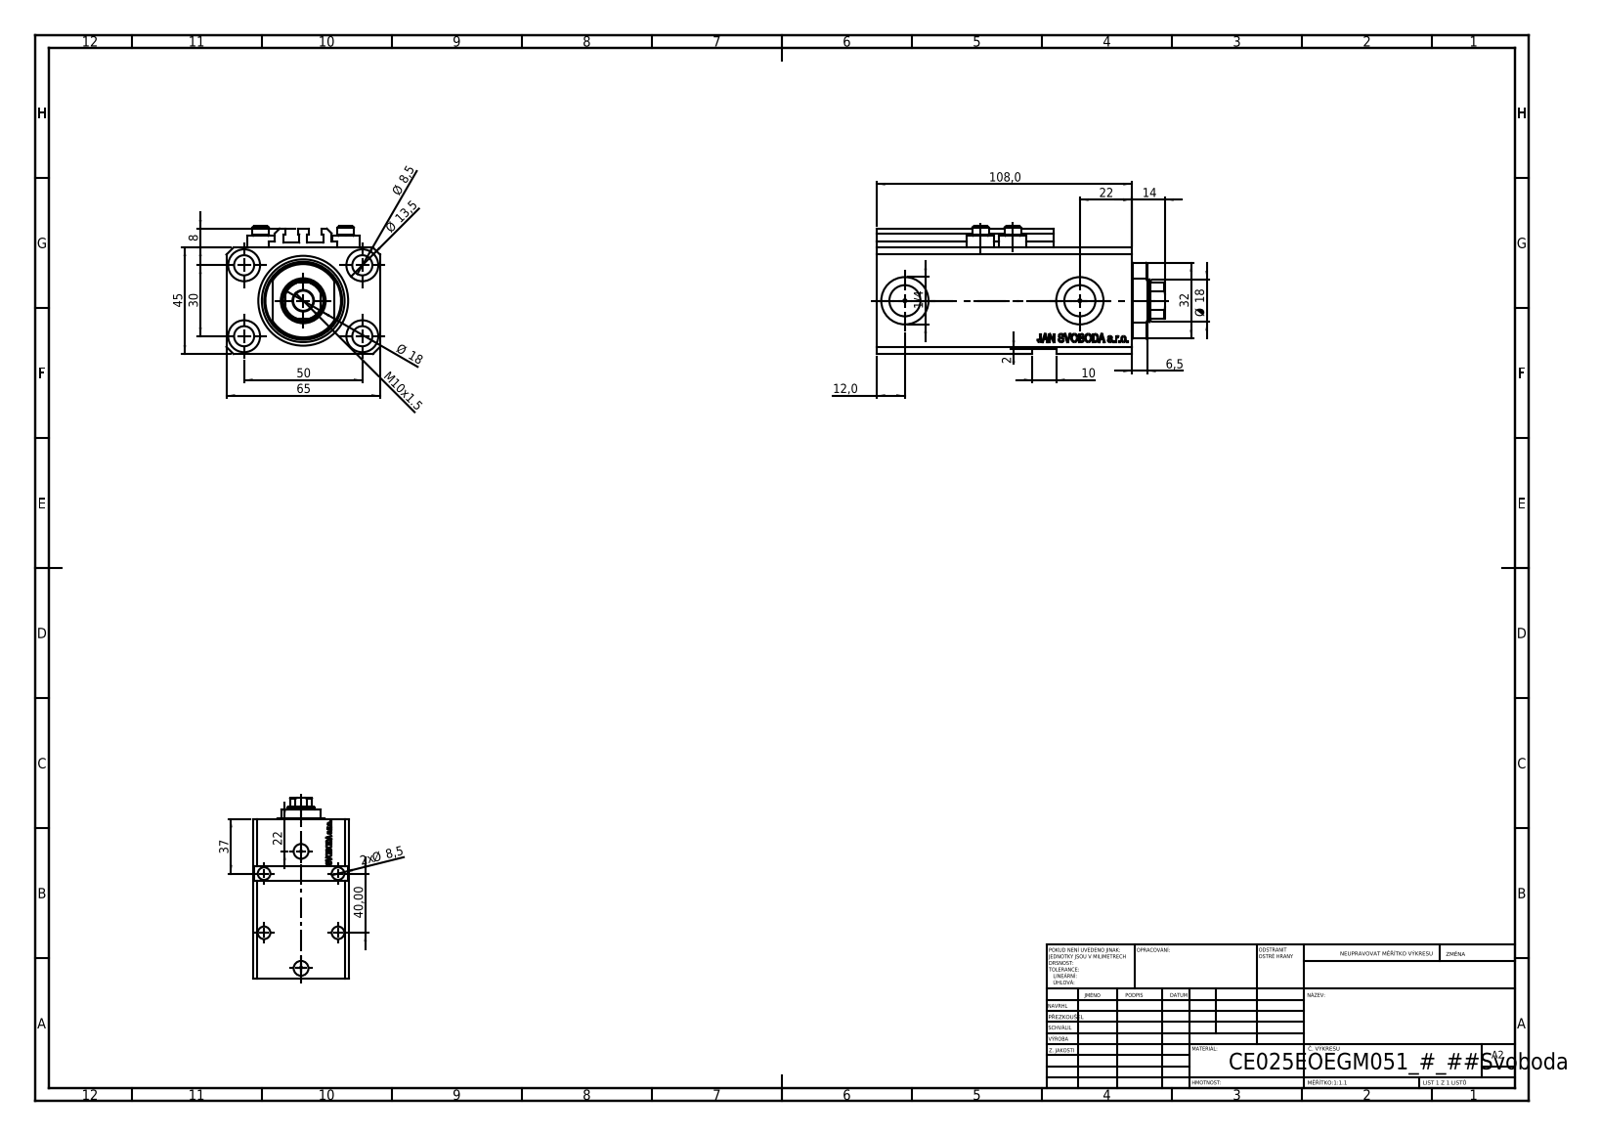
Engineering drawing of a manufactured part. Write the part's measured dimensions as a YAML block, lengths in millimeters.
part_name: "V250CE_C_VCP; ALLEN BOLT V250CE; V250CE_VC_E; V250CE_E_Body"
step_written_by: "SolidWorks 2019 (CONFIG_CONTROL_DESIGN)"
units: millimeters
bodies: {solids: 8, faces: 1087, planar: 511, cylindrical: 146, other: 430}
overall_size: [122, 65, 54]
volume: 275969
surface_area: 77432
round_holes:
  - {diameter: 8.5, count: 9}
  - {diameter: 1.25, count: 4}
  - {diameter: 4, count: 4}
  - {diameter: 13.5, count: 4}
  - {diameter: 10, count: 2}
  - {diameter: 13.16, count: 2}
  - {diameter: 20, count: 2}
  - {diameter: 18, count: 1}
  - {diameter: 25, count: 1}
  - {diameter: 38, count: 1}
round_bosses_or_shafts:
  - {diameter: 11.6, count: 4}
  - {diameter: 7, count: 4}
partial_cylinders:
  - {radius: 0.2, count: 10}
  - {radius: 8.5, count: 1}
  - {radius: 16, count: 1}
face_to_face_distances: [45, 65, 94, 2, 47, 14, 108, 2.5, 10, 20.5]
hole_center_spacings: [29.15, 50, 13.6, 14.76, 15.12, 27.51, 27.89, 30]
